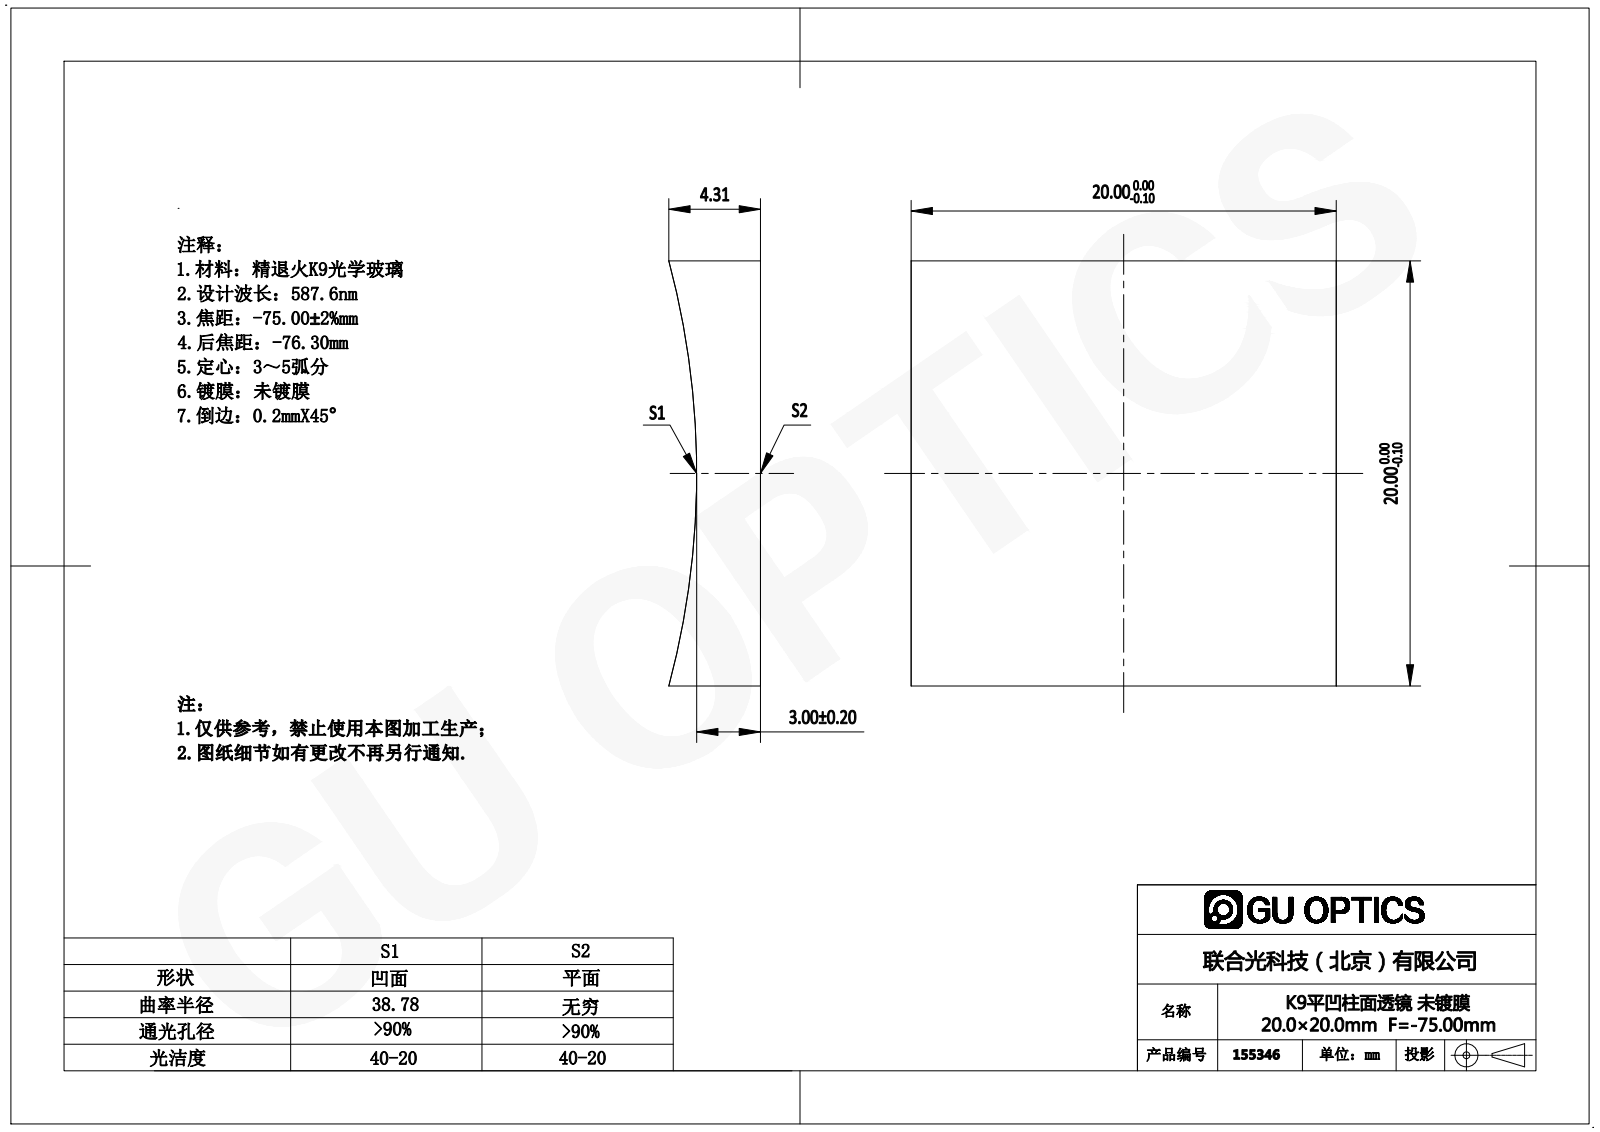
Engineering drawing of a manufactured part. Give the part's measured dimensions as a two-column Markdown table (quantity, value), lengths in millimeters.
| quantity | value |
| --- | --- |
| part name | 155346 |
| STEP written by | SolidWorks 2016 (AUTOMOTIVE_DESIGN) |
| units | millimeters |
| bodies | 1 solid, 6 faces (5 planar, 1 cylindrical, 0 other) |
| overall size | 20 × 20 × 4.31 |
| volume | 1 374 mm³ |
| surface area | 1 114 mm² |
| partial cylindrical surfaces (radius × count) | 38.78 × 1 |
| main face-to-face distances | 20 |
